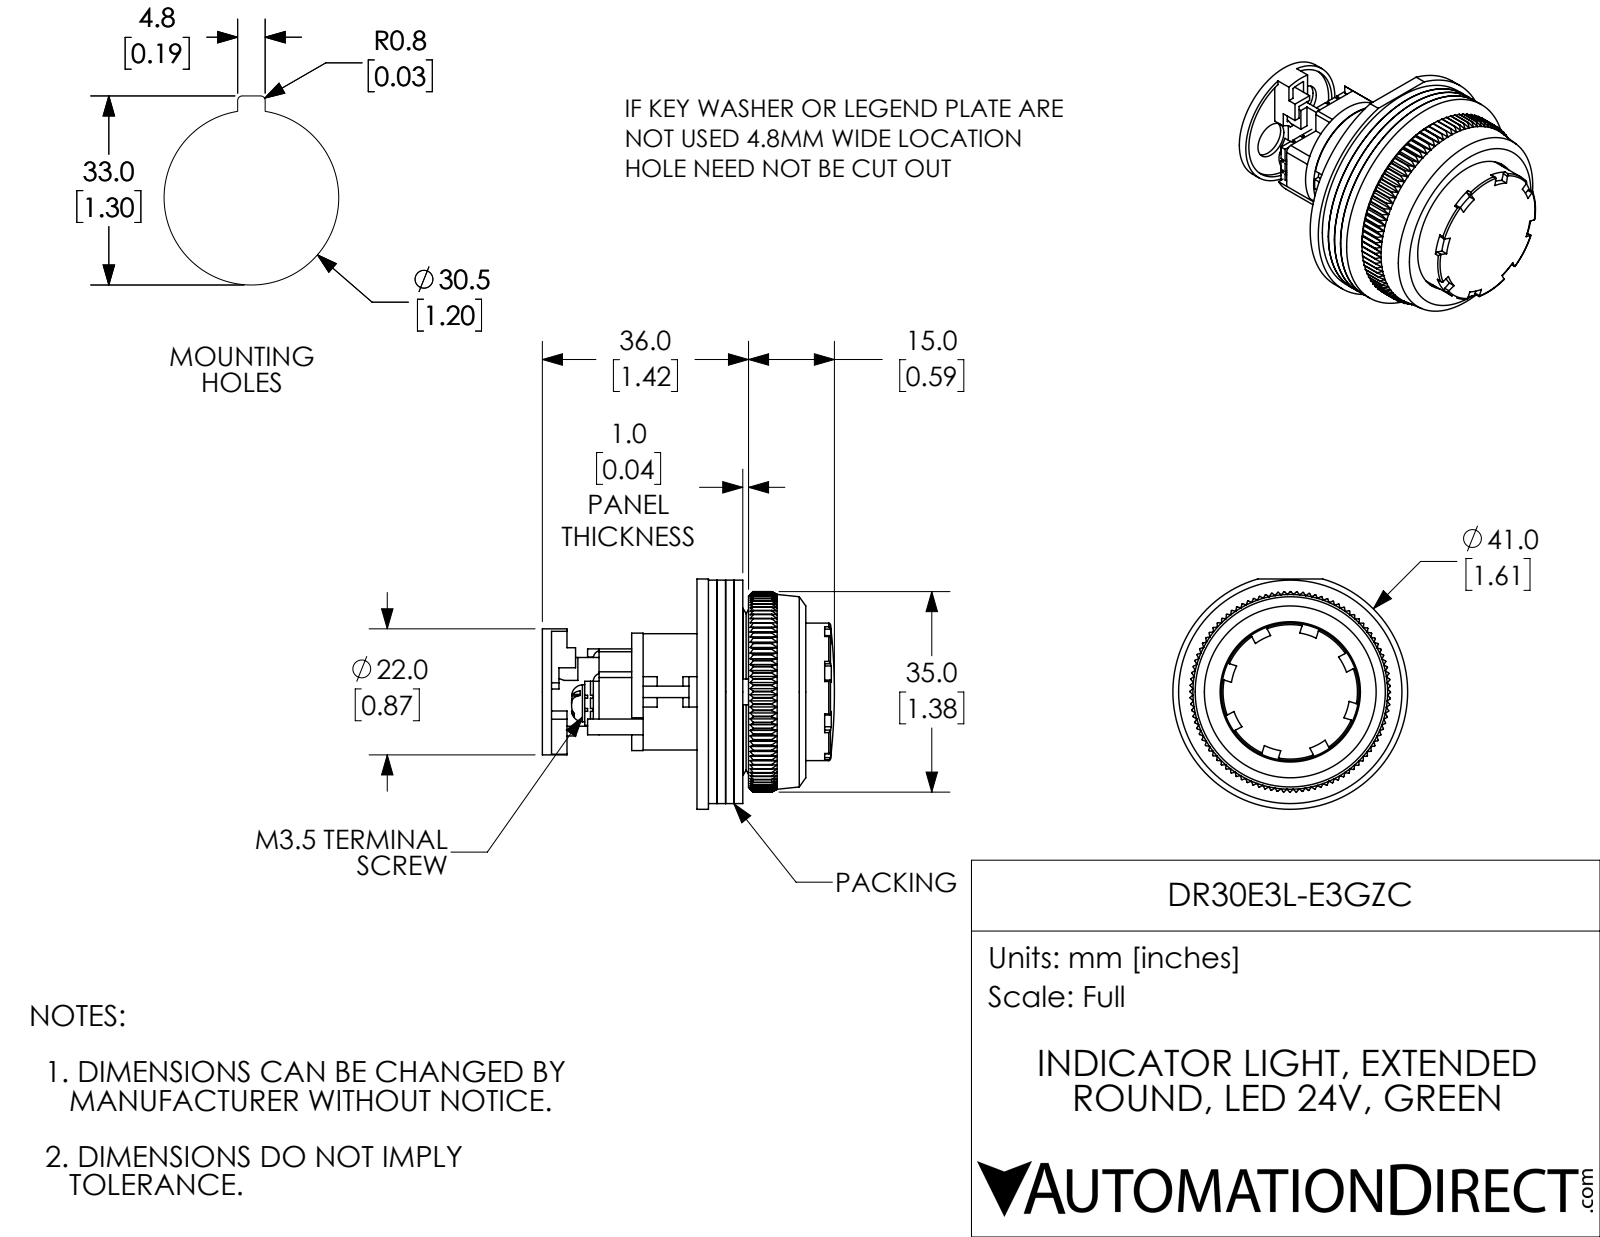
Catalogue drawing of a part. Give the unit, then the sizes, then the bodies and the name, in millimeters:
Units: millimetres
Overall size (bounding box): 51 × 41 × 40.2
Round holes (diameter × count): ⌀3 ×2, ⌀3.5 ×2, ⌀6.4 ×2, ⌀14.3 ×1, ⌀16 ×1, ⌀18.3 ×1, ⌀20 ×1, ⌀20.5 ×1, ⌀22 ×1, ⌀24.5 ×1, ⌀28.5 ×1, ⌀29.8 ×1
Round bosses / shafts (diameter × count): ⌀1.6 ×2, ⌀41 ×1, ⌀39 ×1, ⌀29.5 ×1, ⌀24 ×1, ⌀21.8 ×1, ⌀20.8 ×1, ⌀20.3 ×1
Partial cylindrical surfaces — rounded edges, fillets, slot ends (radius × count): R0.3 ×16, R1.5 ×8, R0.3 ×5, R0.6 ×5, R0.4 ×4, R1.4 ×4, R0.5 ×2, R1 ×2
Main face-to-face distances: 1.5, 3, 4.5, 1, 5, 2, 8, 6.5, 2.5, 6
Hole centre spacings: 4.5, 4.7, 9.2, 8.9, 9.4
Volume: 17 570 mm³ · Surface area: 24 230 mm²
Bodies: 16 solids, 1287 faces (717 planar, 328 cylindrical, 242 other)
Part name (STEP PRODUCT): DR30E3L-E3GZC
STEP written by: SolidWorks 2017 (AUTOMOTIVE_DESIGN)
